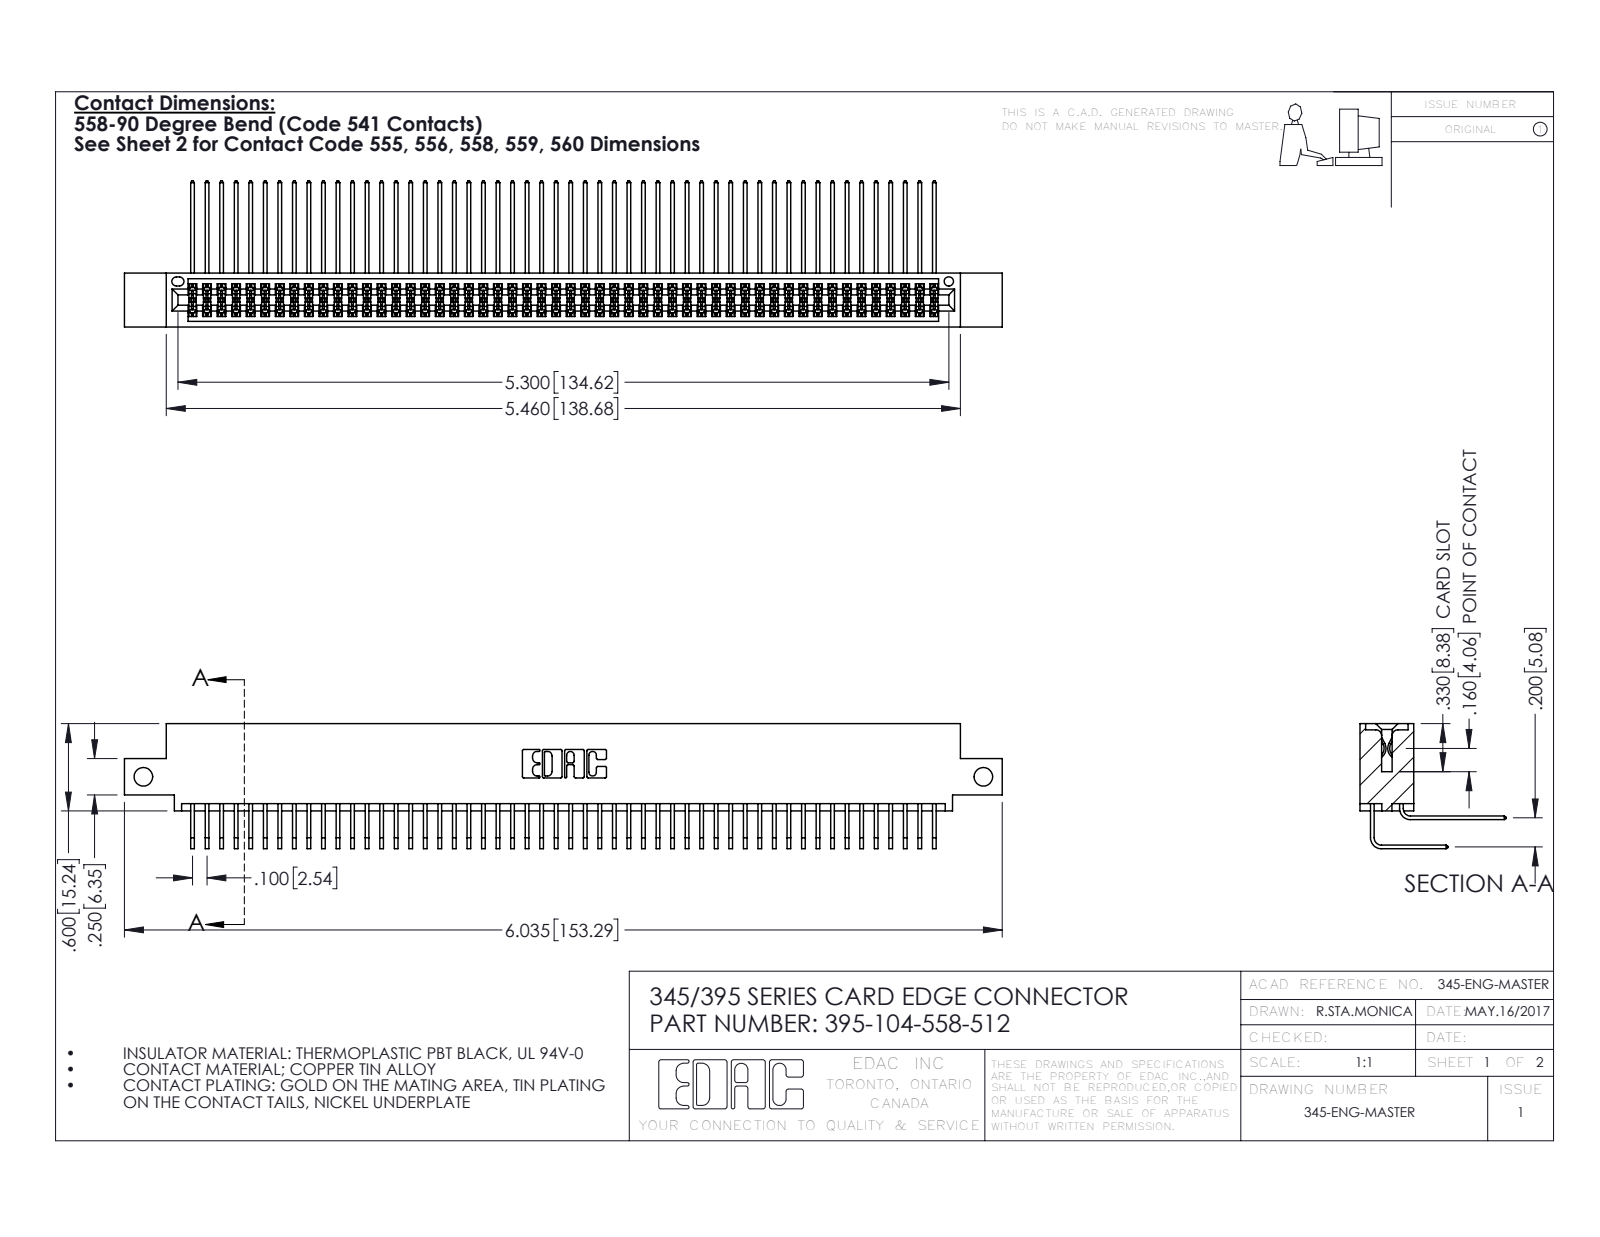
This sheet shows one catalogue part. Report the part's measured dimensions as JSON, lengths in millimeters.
{"part_name": "345-292-001_558 559 Tail - 1; 395-104-558-512; 345 Part_0.110 Offset - Side Mount; 345-292-001_558 Tail - 2", "step_written_by": "SolidWorks 2016 (CONFIG_CONTROL_DESIGN)", "units": "millimeters", "bodies": {"solids": 105, "faces": 5538, "planar": 3724, "cylindrical": 1814, "other": 0}, "overall_size": [153.3, 25.5, 21.8], "volume_mm3": 15400, "surface_area_mm2": 25770, "round_holes": [[3.3, 2], [1.6, 1]], "partial_cylinders_radius": [[0.2, 157], [0.3, 22], [0.2, 6], [0.8, 6], [0.7, 3], [0.4, 2], [0.5, 2], [0.6, 2]], "face_to_face_distances": [1.8, 7.6, 5.1, 9.4, 2.5, 6.9, 0.6, 5.7, 0.6, 4.4], "hole_center_spacings": [146.7]}
